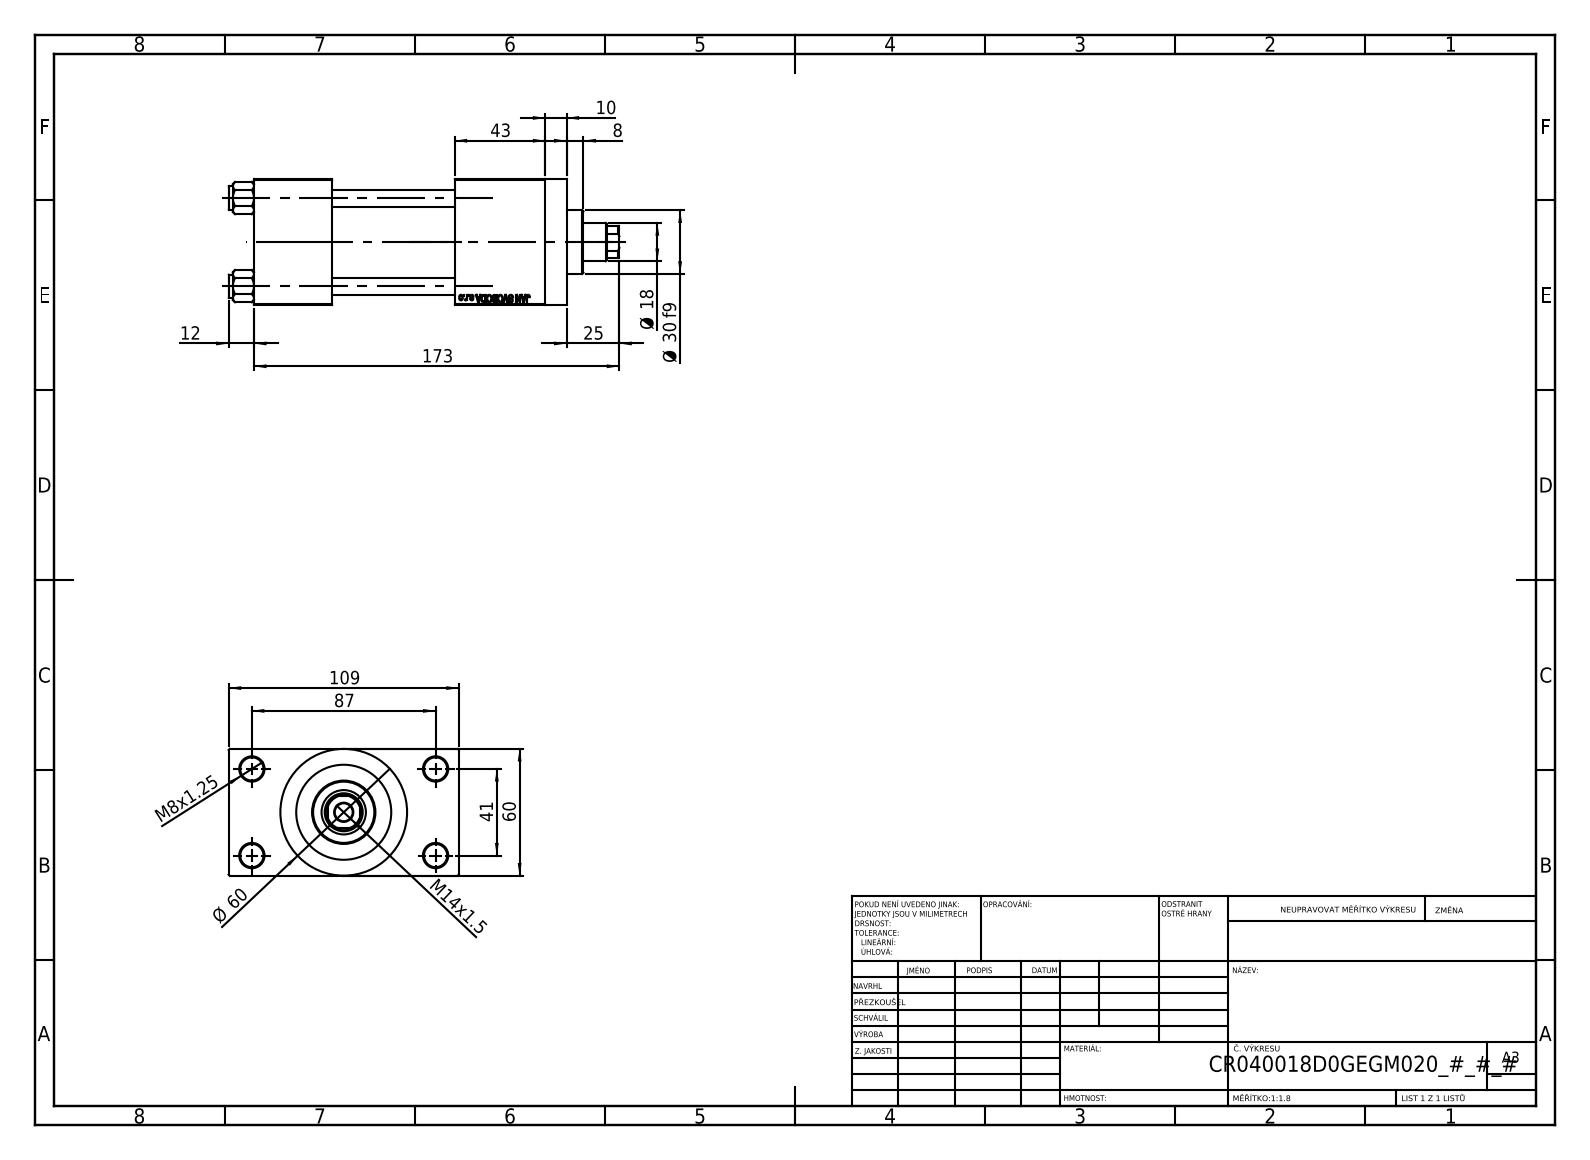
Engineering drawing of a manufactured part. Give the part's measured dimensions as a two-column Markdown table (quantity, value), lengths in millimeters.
| quantity | value |
| --- | --- |
| part name | V215_VC_A; V215CR_VCP_D; V215CR_D_Body; NUT_M5_D (+1 more) |
| STEP written by | SolidWorks 2019 (CONFIG_CONTROL_DESIGN) |
| units | millimeters |
| bodies | 11 solids, 1105 faces (498 planar, 89 cylindrical, 518 other) |
| overall size | 185 × 109 × 60 |
| volume | 517 784 mm³ |
| surface area | 121 264 mm² |
| round holes (diameter × count) | 8 × 4, 11 × 4, 7 × 2, 16.66 × 2, 24 × 2, 8.5 × 1, 18 × 1, 21 × 1, 31 × 1, 40 × 1, 45 × 1 |
| round bosses / shafts (diameter × count) | 11 × 4, 60 × 1, 46 × 1, 30 × 1 |
| partial cylindrical surfaces (radius × count) | 8.5 × 1 |
| main face-to-face distances | 60, 24.5, 84.5, 58, 37, 95, 138, 101, 43, 109 |
| hole center spacings | 22.65, 29.49, 41.7, 47.15, 48.09, 64.35, 76.49, 41 |
